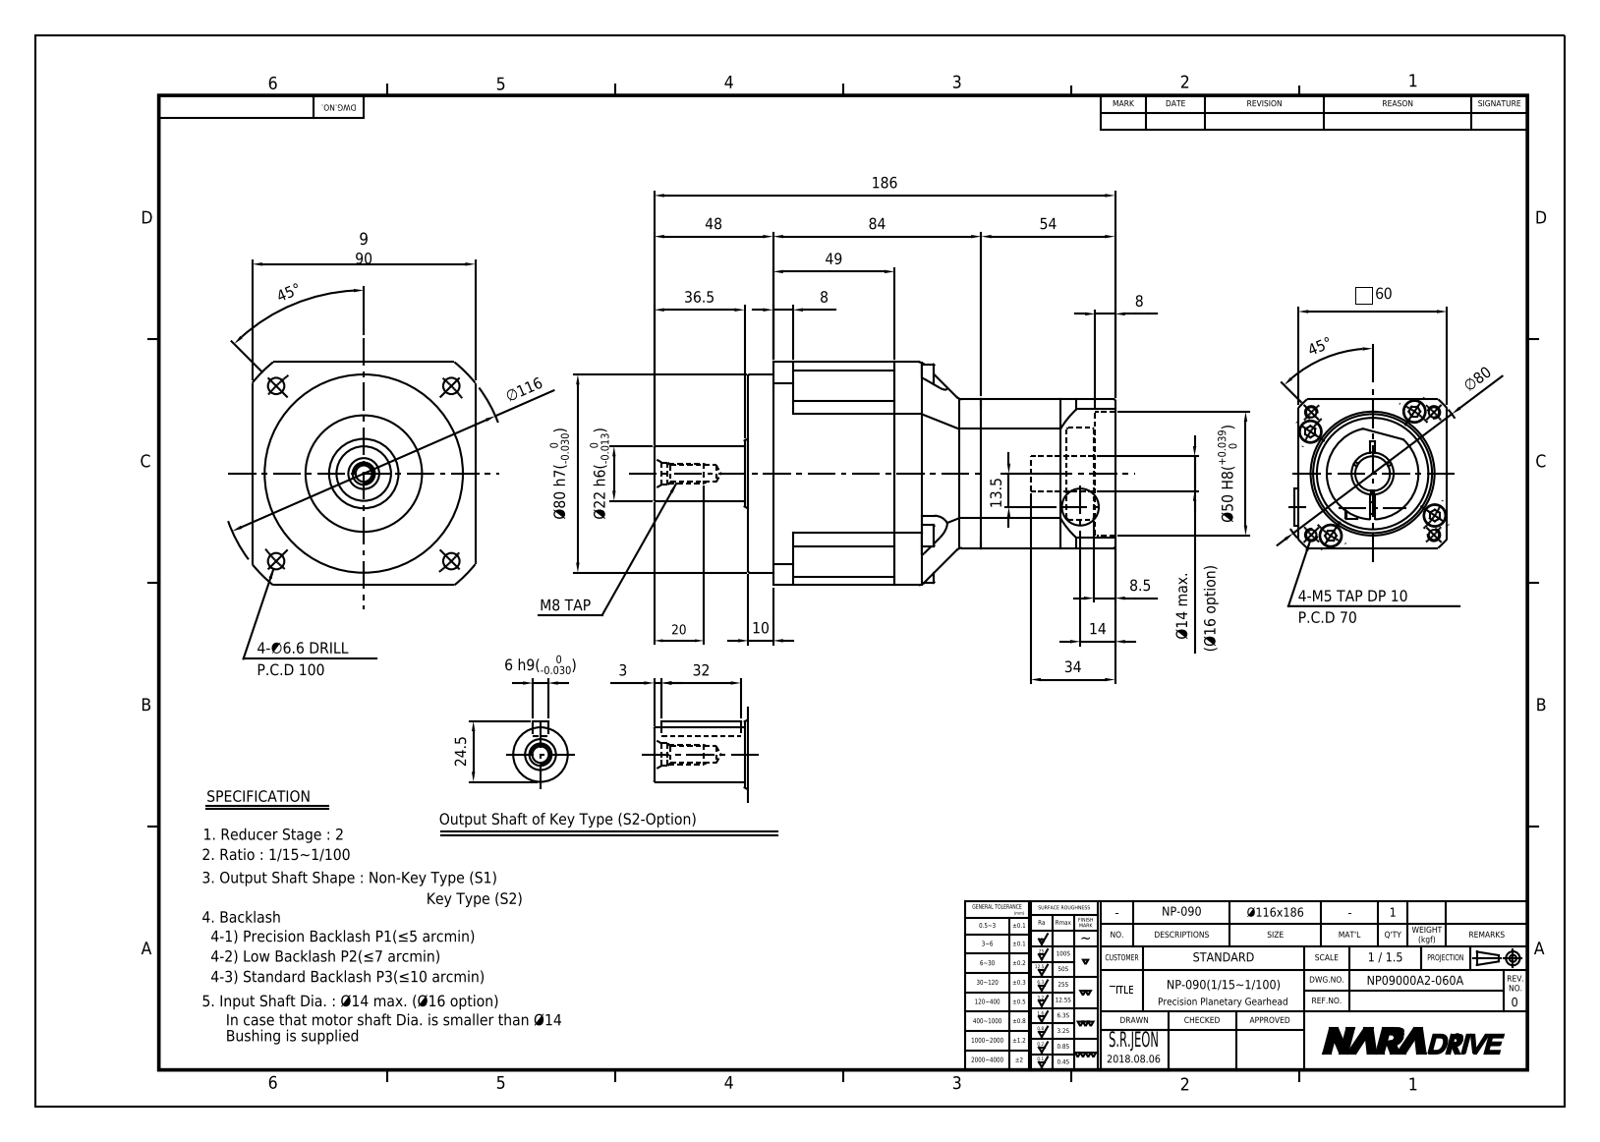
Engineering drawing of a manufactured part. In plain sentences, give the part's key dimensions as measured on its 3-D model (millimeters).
The part is named "NP09000A2-060A-S1". Its 3-D file was written by "Autodesk Inventor 2015 (AUTOMOTIVE_DESIGN)". It is 2 solids with 444 faces: 204 planar, 126 cylindrical and 114 other. Overall it measures 186 by 90 by 90 millimeters. Its volume is 565 299 cubic millimeters and its surface area 101 423 square millimeters. Round holes: 12 of diameter 4.13, 9 of diameter 5.5, 5 of diameter 9, 4 of diameter 3.24, 4 of diameter 4.2, 4 of diameter 6.6, 4 of diameter 7.5, 1 of diameter 6.65, 1 of diameter 7, 1 of diameter 8.5, 1 of diameter 14, 1 of diameter 17. Round bosses or shafts: 9 of diameter 8.5, 9 of diameter 5, 1 of diameter 80, 1 of diameter 37, 1 of diameter 22, 1 of diameter 15, 1 of diameter 8. Partial cylindrical surfaces (rounded edges, fillets, slot ends): 8 of radius 3, 8 of radius 10, 4 of radius 0.5, 1 of radius 2.07, 1 of radius 4.5, 1 of radius 35, 1 of radius 51, 1 of radius 58. The main face-to-face distances are 75, 15, 90, 8, 51, 60, 41, 10, 59, 49. The hole center spacings are 30.25, 8.77, 15.73, 35, 40.79, 42.5, 42.78, 42.79.
